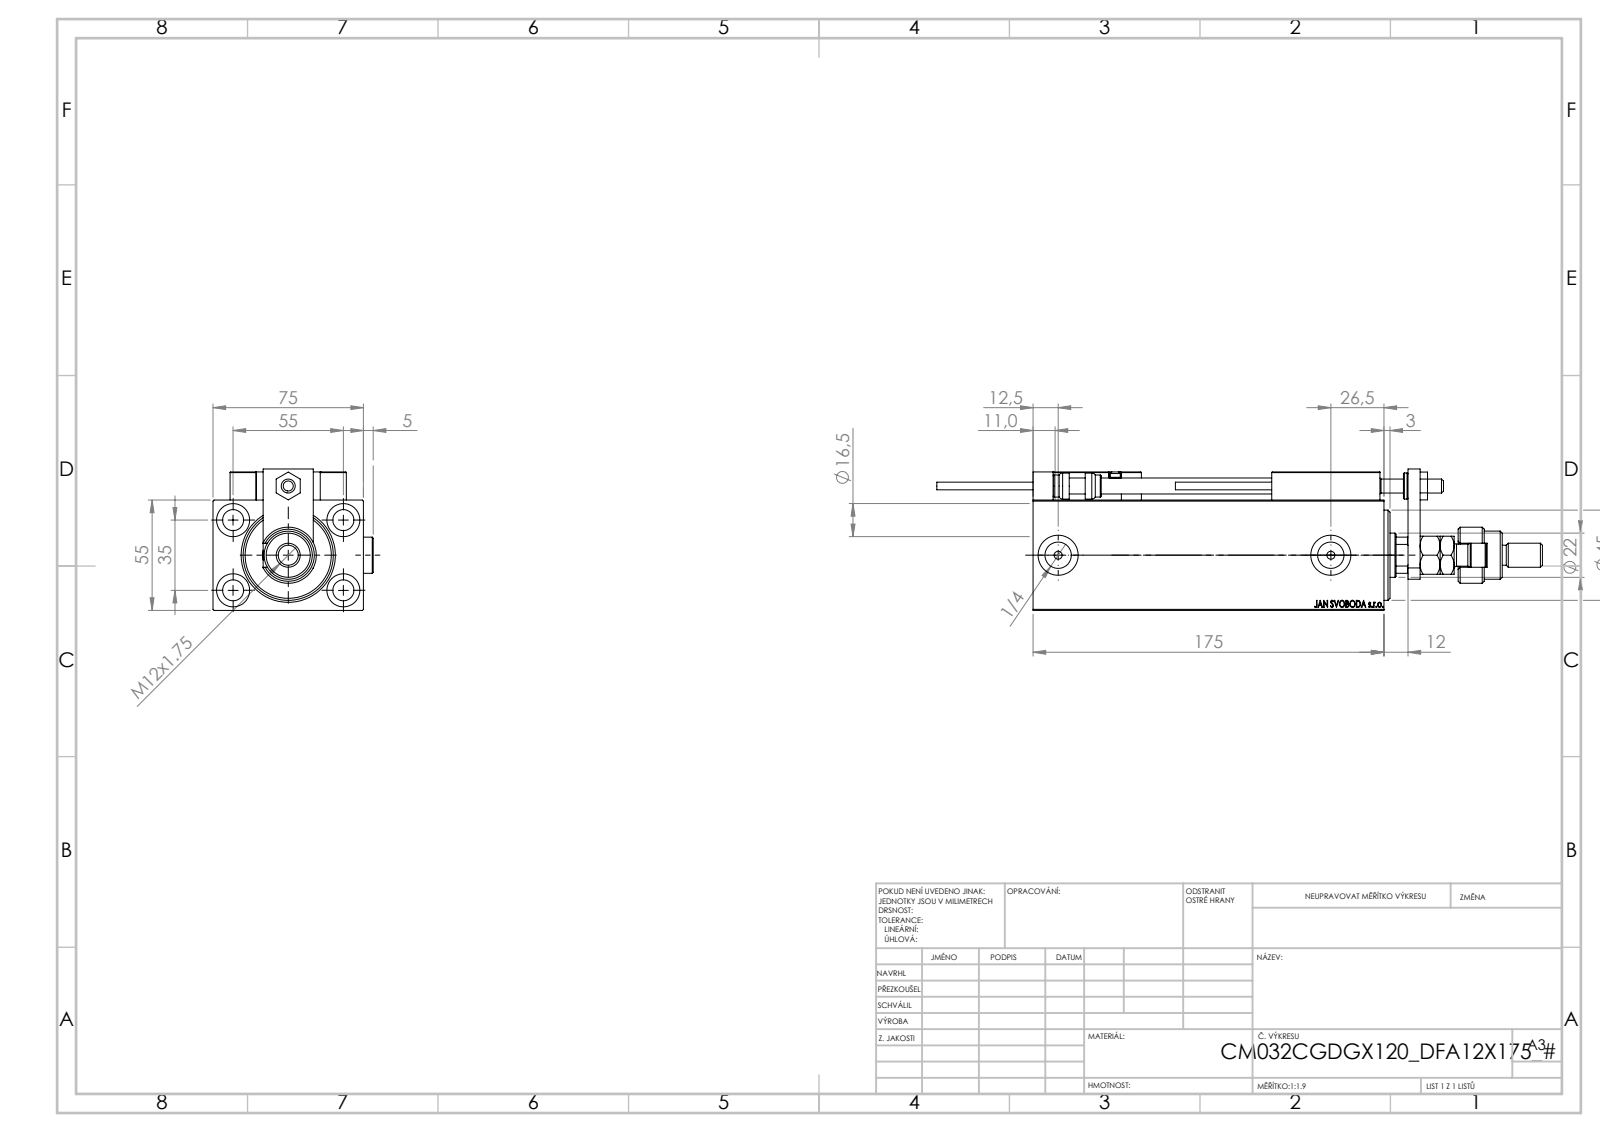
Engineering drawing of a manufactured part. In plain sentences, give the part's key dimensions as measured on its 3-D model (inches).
The part is named "V450CM_C_Body; Zatka_OIL_PORT; KONCOVKA; V450CM_C_VCP (+7 more)". Its 3-D file was written by "SolidWorks 2019 (CONFIG_CONTROL_DESIGN)". It is 27 solids with 1421 faces: 622 planar, 217 cylindrical and 582 other. Overall it measures 11.89 by 3.146 by 2.776 inches. Its volume is 40.89 cubic inches and its surface area 237.3 square inches. Round holes: 6 of diameter 0.157, 5 of diameter 0.315, 5 of diameter 0.413, 5 of diameter 0.65, 4 of diameter 0.126, 2 of diameter 0.197, 2 of diameter 0.518, 2 of diameter 0.787, 1 of diameter 0.276, 1 of diameter 0.866, 1 of diameter 1.004, 1 of diameter 1.26. Round bosses or shafts: 3 of diameter 0.709, 2 of diameter 0.433, 2 of diameter 0.197, 2 of diameter 0.15, 1 of diameter 1.102, 1 of diameter 0.945, 1 of diameter 0.512, 1 of diameter 0.472. Partial cylindrical surfaces (rounded edges, fillets, slot ends): 30 of radius 0.012, 2 of radius 0.118, 1 of radius 0.384, 1 of radius 0.413. The main face-to-face distances are 2.165, 2.953, 0.551, 0.472, 0.394, 0.709, 0.984, 0.197, 0.236, 0.276. The hole center spacings are 1.283, 0.448, 0.787, 1.165, 1.169, 1.273, 1.378, 1.42.
